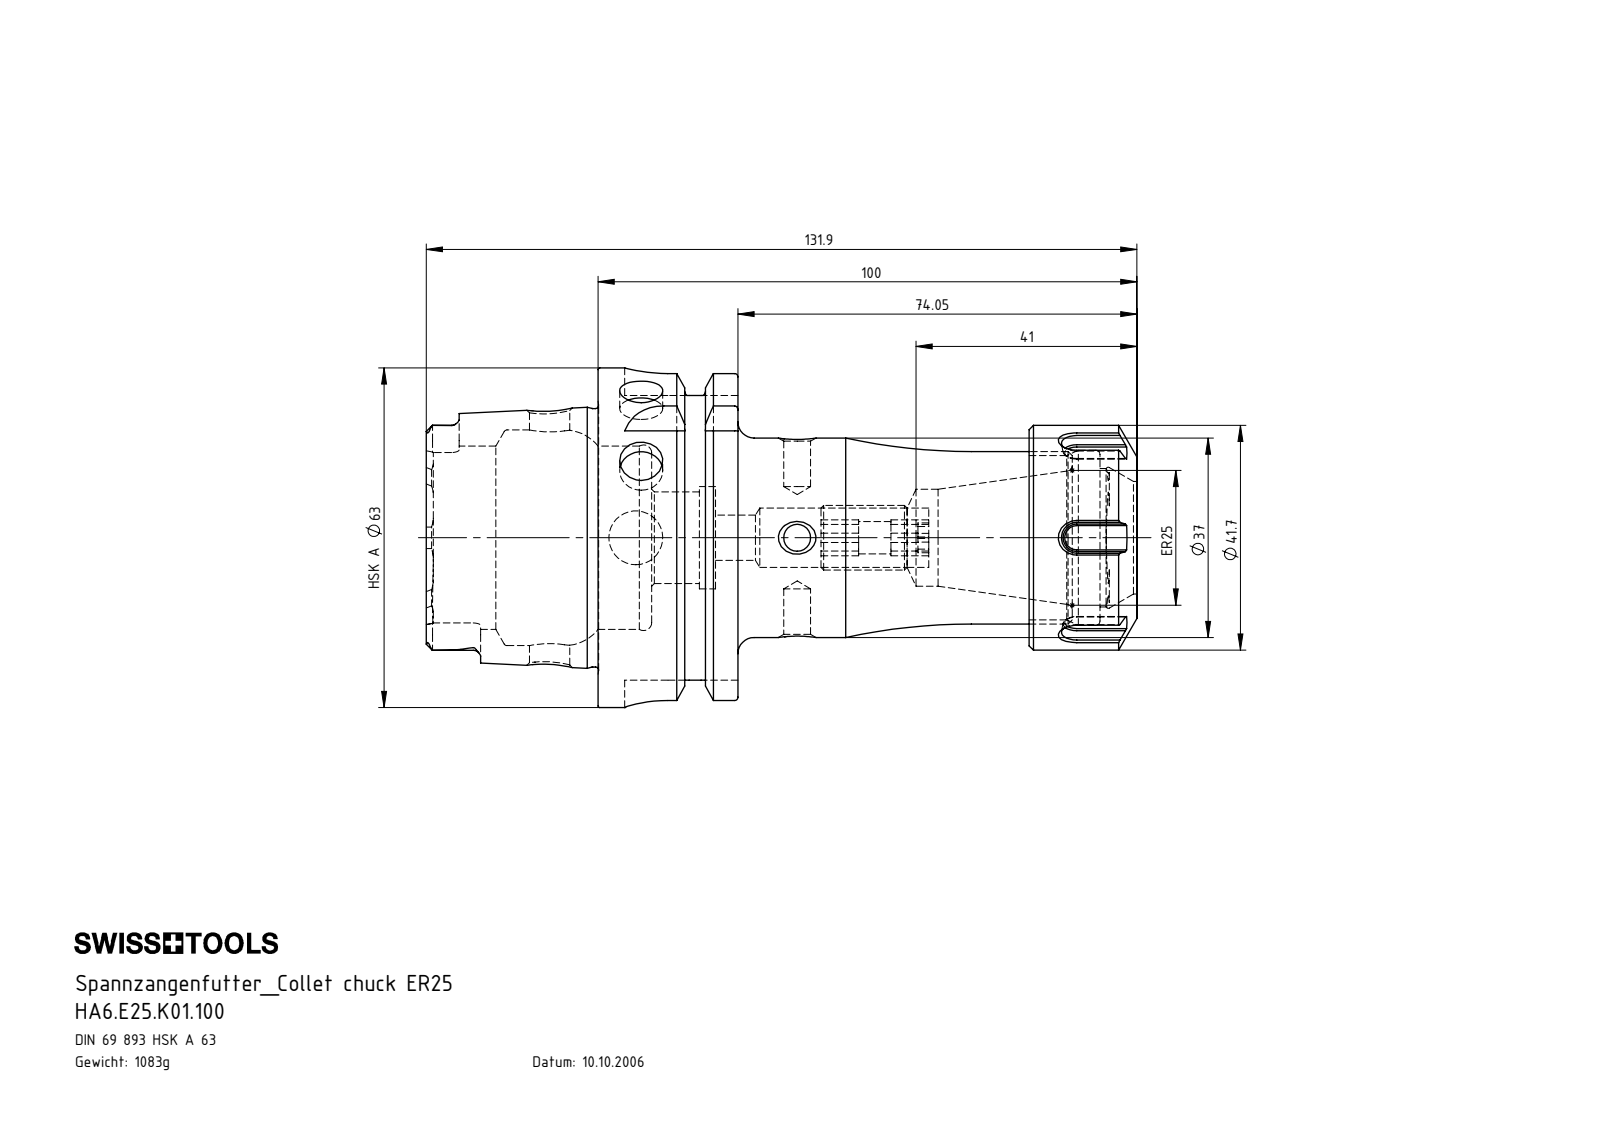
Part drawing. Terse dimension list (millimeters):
name: HA6-E25.K01.100_C_Fertigbearbeitung; E25-ER1.001.020; HA6.E25.K01.100; ERU-AN5.K01.020_A
written by: SolidWorks 2017 (CONFIG_CONTROL_DESIGN)
unit: mm
bodies: 3 solids, 351 faces (131 planar, 80 cylindrical, 140 other)
size: 131.9 × 63 × 63
volume: 137 916 mm³; area: 39 497 mm²
holes: 2× ⌀5, 2× ⌀8, 1× ⌀6, 1× ⌀7.5, 1× ⌀8.4, 1× ⌀10, 1× ⌀11, 1× ⌀17, 1× ⌀18, 1× ⌀19, 1× ⌀20.9, 1× ⌀30.5
bosses: 1× ⌀63, 1× ⌀54.95, 1× ⌀47.94, 1× ⌀41.7, 1× ⌀37, 1× ⌀32, 1× ⌀12
rounds: 6× R1.4, 4× R2.88, 4× R8, 2× R12.17
face distances: 25.95, 16, 80, 54.05, 9.95, 70.05, 20, 100, 90.05, 74.05
hole spacings: 29.95, 45.95
